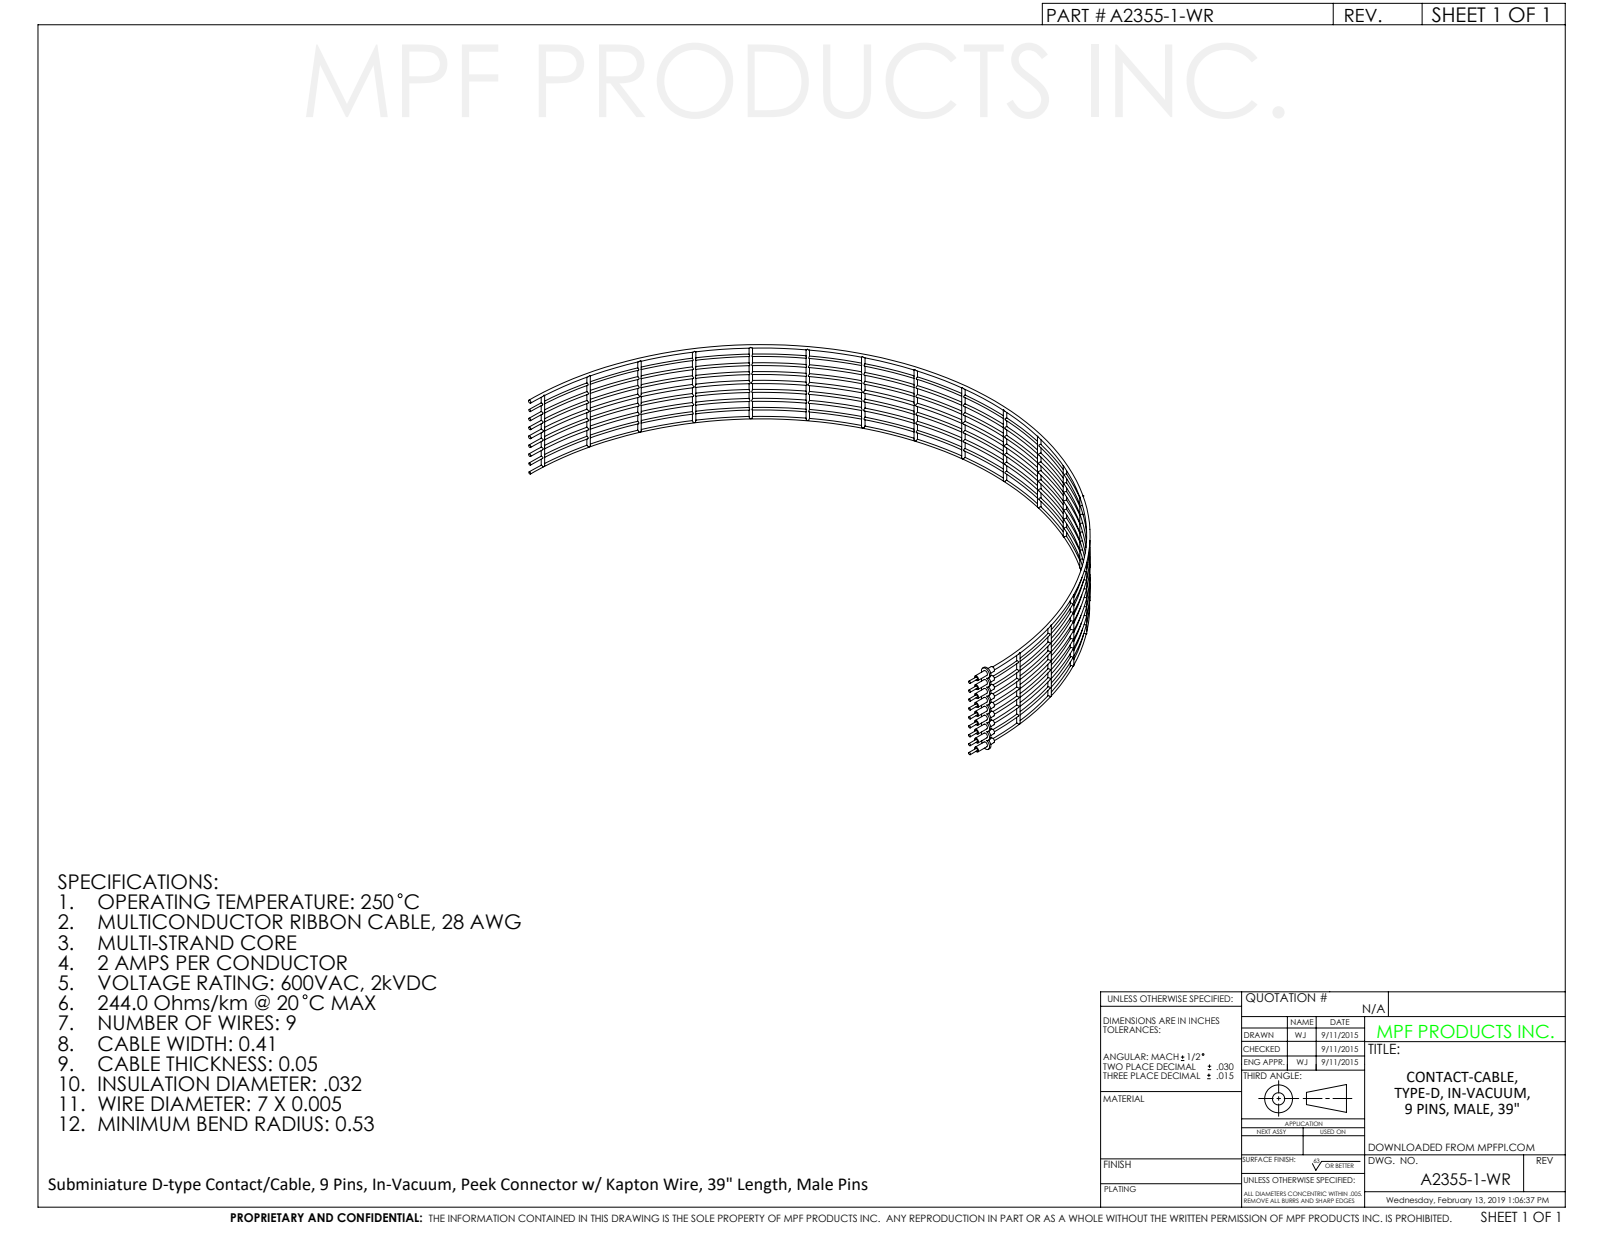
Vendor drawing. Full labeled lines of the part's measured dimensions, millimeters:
Part name (STEP PRODUCT): A2355-1-WR
STEP written by: SolidWorks 2012 (CONFIG_CONTROL_DESIGN)
Units: millimetres
Bodies: 1 solid, 515 faces (75 planar, 116 cylindrical, 324 other)
Overall size (bounding box): 154.1 × 84.2 × 23
Volume: 1 000 mm³ · Surface area: 5 526 mm²
Round bosses / shafts (diameter × count): ⌀0.8 ×18, ⌀1.3 ×9, ⌀0.6 ×9, ⌀2.7 ×8
Partial cylindrical surfaces — rounded edges, fillets, slot ends (radius × count): R1.3 ×1
Main face-to-face distances: 0.5, 1.9, 2.3, 5.3, 3.4, 2.9, 7.6, 5.7, 5.3, 2.3
